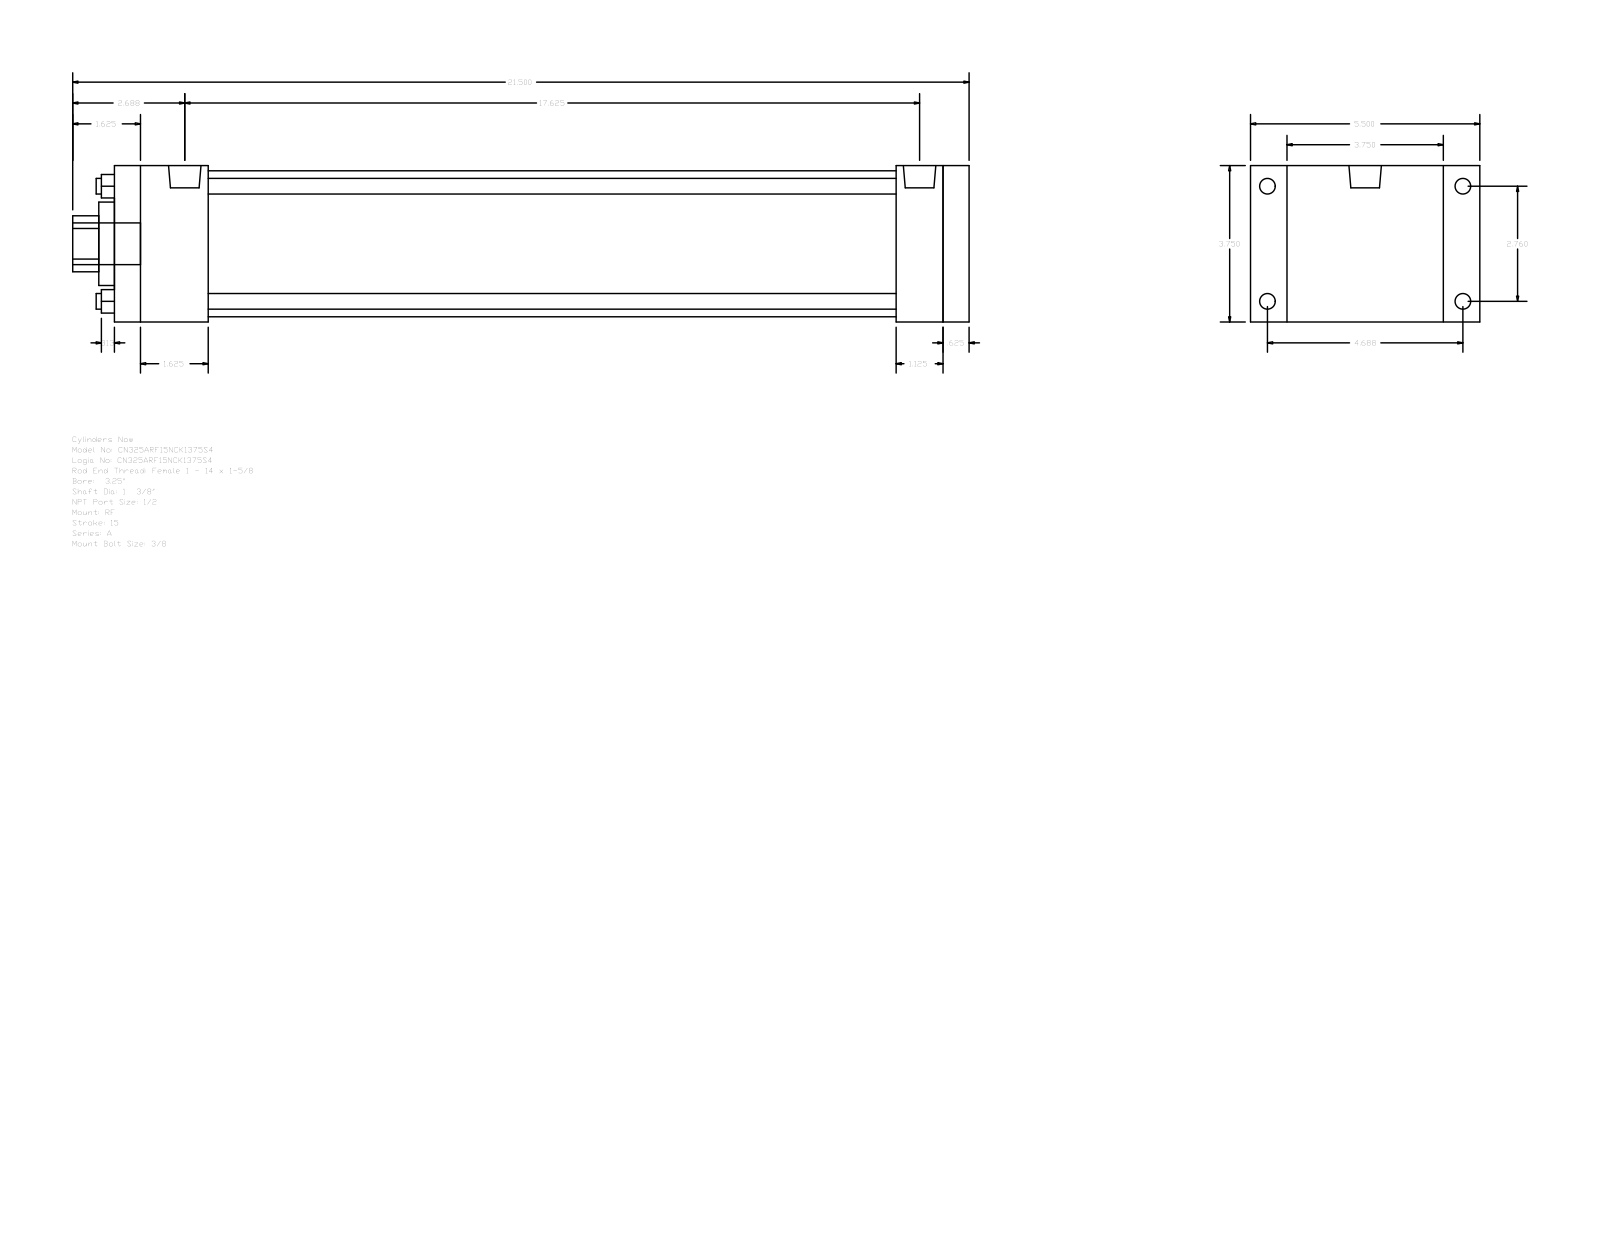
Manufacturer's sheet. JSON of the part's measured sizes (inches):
{"part_name": "A_RF__0325_1.375", "step_written_by": "GSSL Pune (CONFIG_CONTROL_DESIGN)", "units": "inches", "bodies": {"solids": 0, "faces": 92, "planar": 64, "cylindrical": 28, "other": 0}, "overall_size": [21.5, 5.5, 3.75], "round_holes": [[0.375, 4], [1.375, 1], [2, 1], [3.5, 1]], "round_bosses_or_shafts": [[0.375, 4], [0.344, 4], [0.778, 2], [1, 1]], "partial_cylinders_radius": [[0.672, 1]], "face_to_face_distances": [3.75, 20.5, 0.625, 19.875, 1.125, 0.875, 4.625, 18.75, 1.75, 2.25], "hole_center_spacings": [1.952, 2.76, 3.903]}
